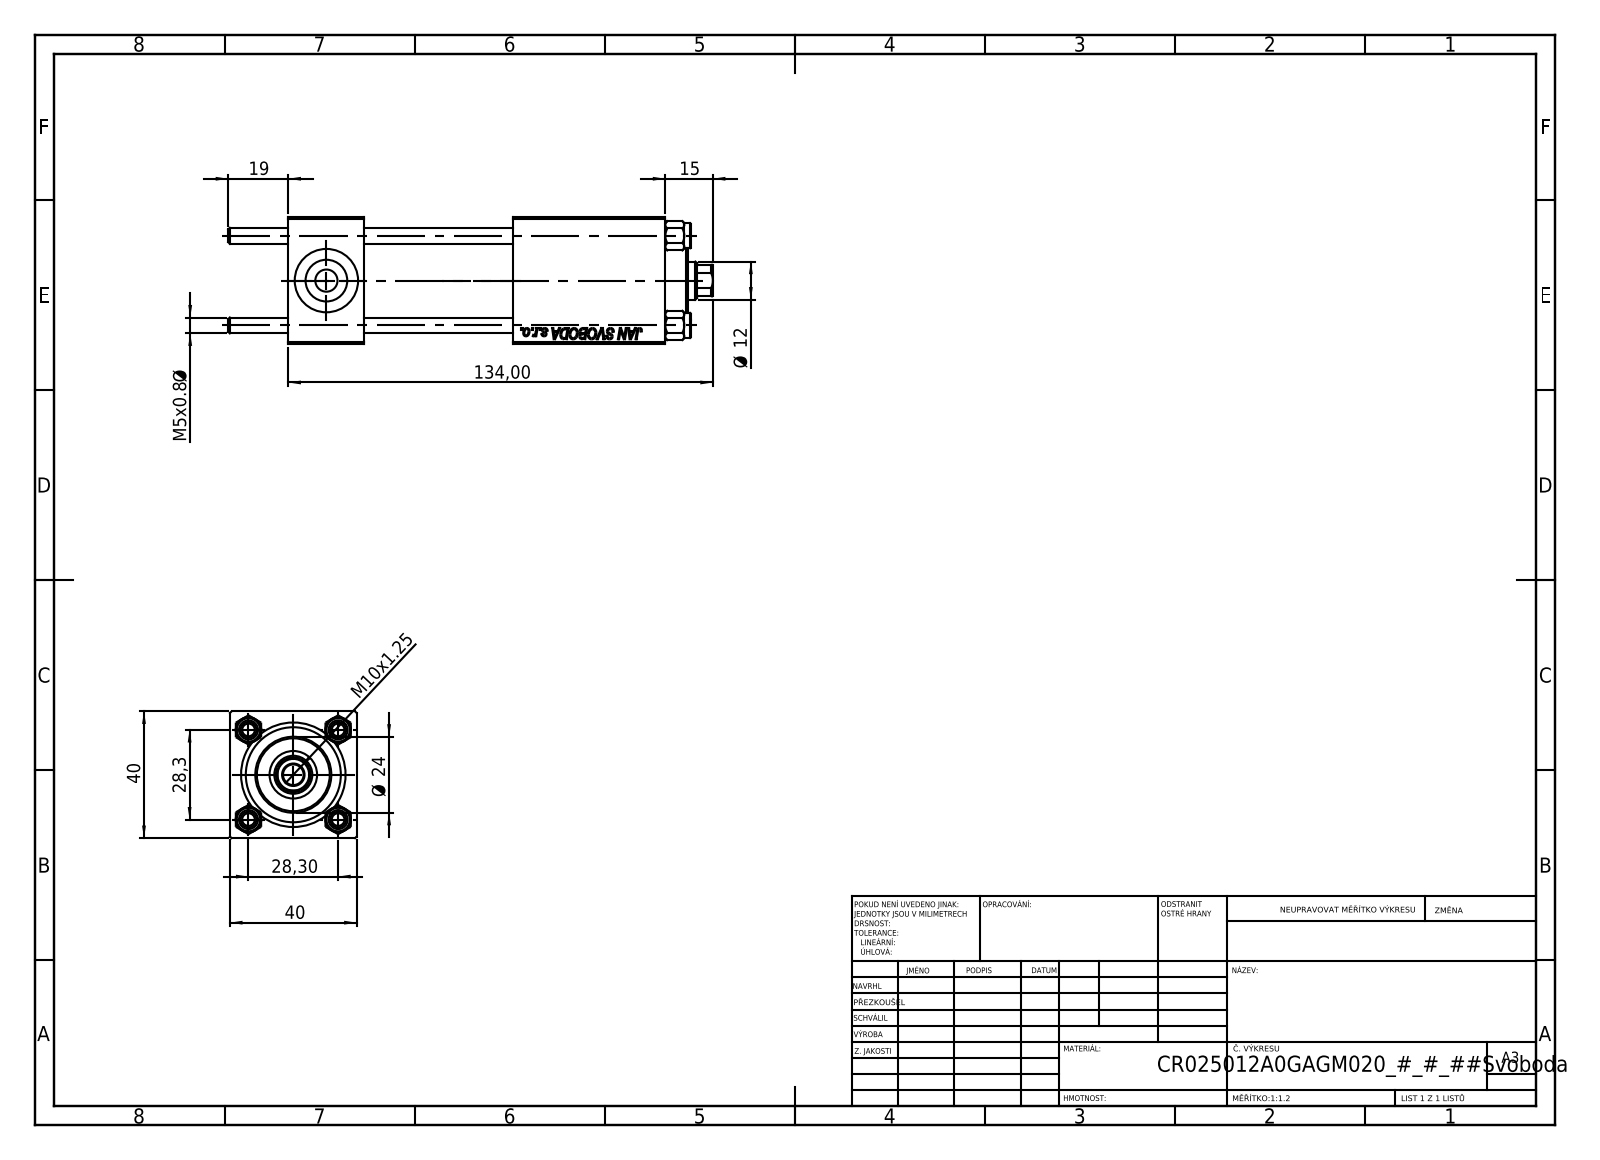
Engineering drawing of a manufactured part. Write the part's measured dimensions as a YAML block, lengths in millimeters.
part_name: "V215CR_VCP; CR025_012_A_0_G_A_G_M_020_+#_##_TYCINKA; V215_VC_A; NUT_M5 (+1 more)"
step_written_by: "SolidWorks 2019 (CONFIG_CONTROL_DESIGN)"
units: millimeters
bodies: {solids: 11, faces: 1132, planar: 517, cylindrical: 79, other: 536}
overall_size: [153, 40, 40]
volume: 144743
surface_area: 58872
round_holes:
  - {diameter: 5, count: 4}
  - {diameter: 20, count: 3}
  - {diameter: 7, count: 2}
  - {diameter: 13.16, count: 2}
  - {diameter: 6.5, count: 1}
  - {diameter: 12, count: 1}
  - {diameter: 15, count: 1}
  - {diameter: 25, count: 1}
  - {diameter: 30, count: 1}
round_bosses_or_shafts:
  - {diameter: 8, count: 4}
  - {diameter: 31, count: 1}
  - {diameter: 24, count: 1}
partial_cylinders:
  - {radius: 5.5, count: 1}
face_to_face_distances: [40, 24, 119, 95, 90.3, 66.3, 28.7, 71, 47, 19.3]
hole_center_spacings: [20.01, 28.3, 40.02]
